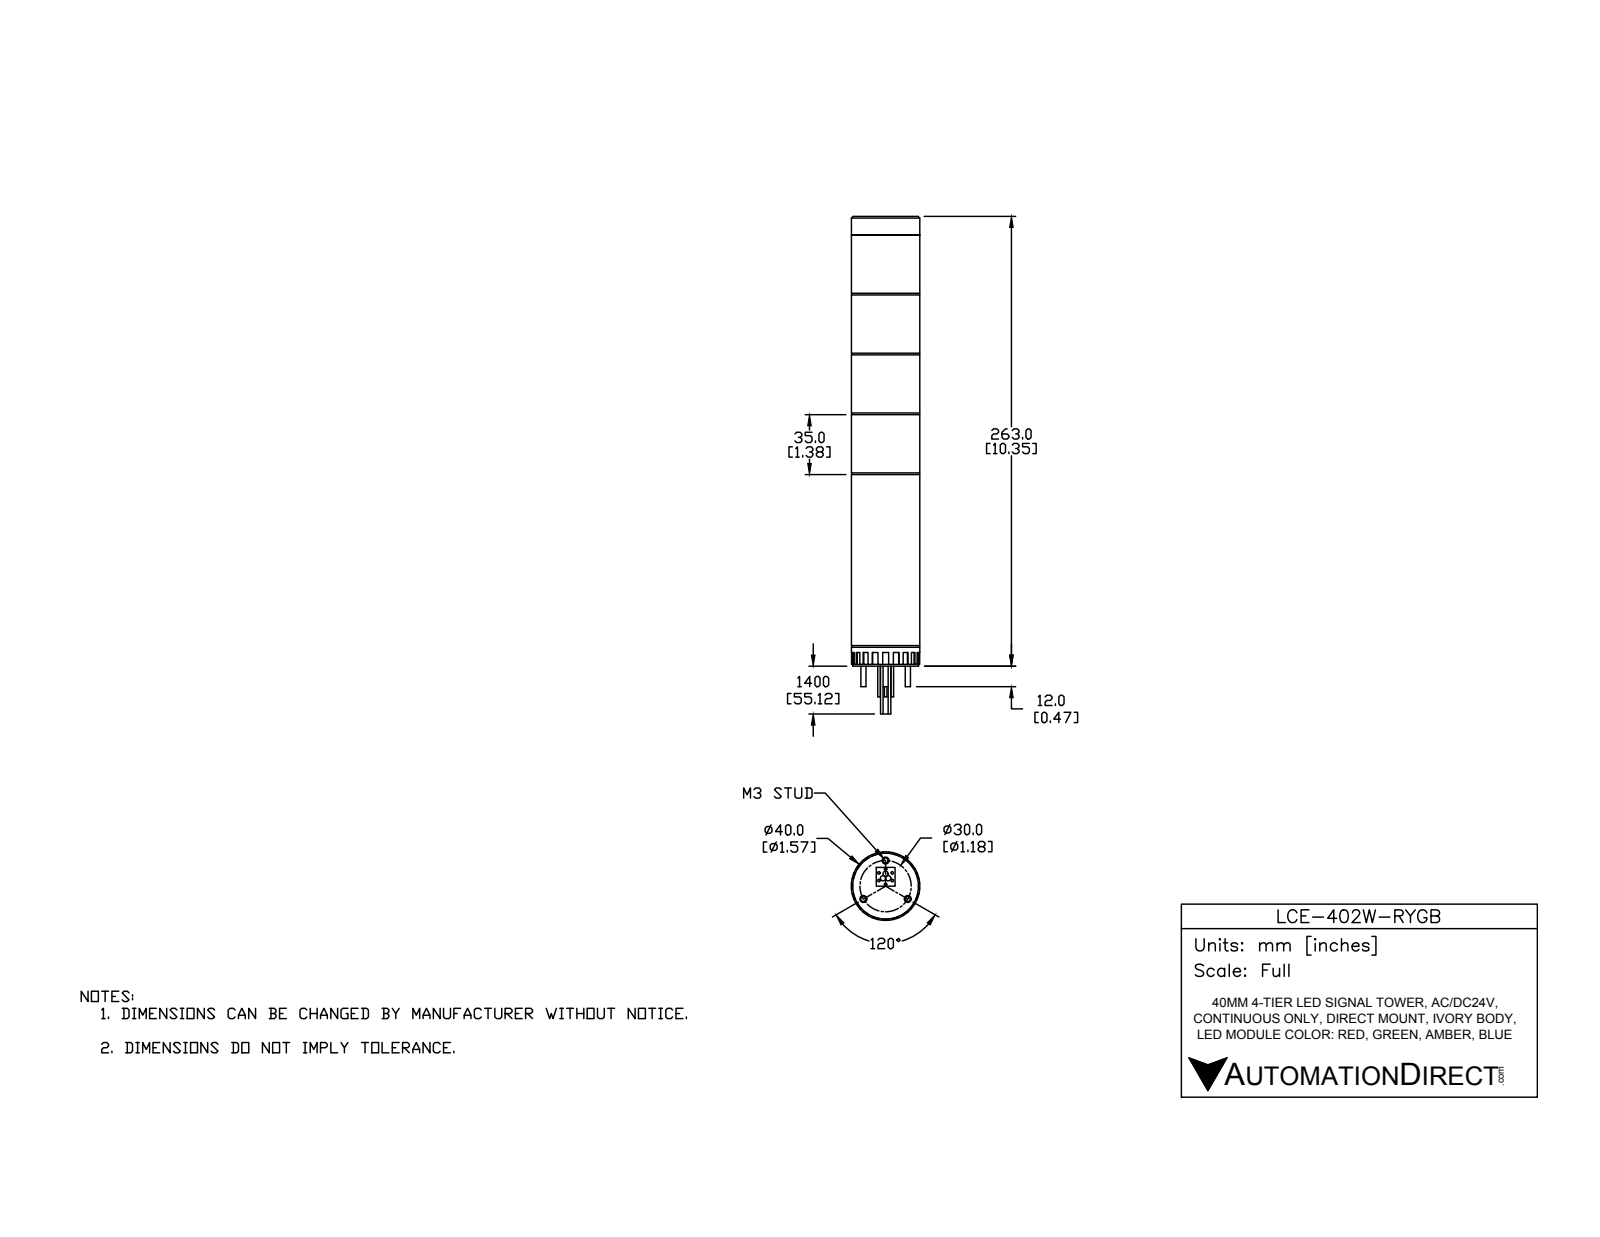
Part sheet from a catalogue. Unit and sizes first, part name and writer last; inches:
Units: inches
Overall size (bounding box): 11.063 × 1.575 × 1.575
Round holes (diameter × count): ⌀0.157 ×3, ⌀0.315 ×1
Round bosses / shafts (diameter × count): ⌀0.059 ×6, ⌀0.118 ×3, ⌀1.575 ×1, ⌀1.555 ×1, ⌀1.516 ×1, ⌀0.217 ×1
Main face-to-face distances: 1.378, 0.039, 2.756, 1.339, 4.134, 1.417, 2.717, 4.094, 2.795, 3.976
Hole centre spacings: 0.591, 1.023
Volume: 20.07 in³ · Surface area: 103.1 in²
Bodies: 23 solids, 210 faces (152 planar, 54 cylindrical, 4 other)
Part name (STEP PRODUCT): LCE-402W-RYGB
STEP written by: SolidWorks 2016 (AUTOMOTIVE_DESIGN)
